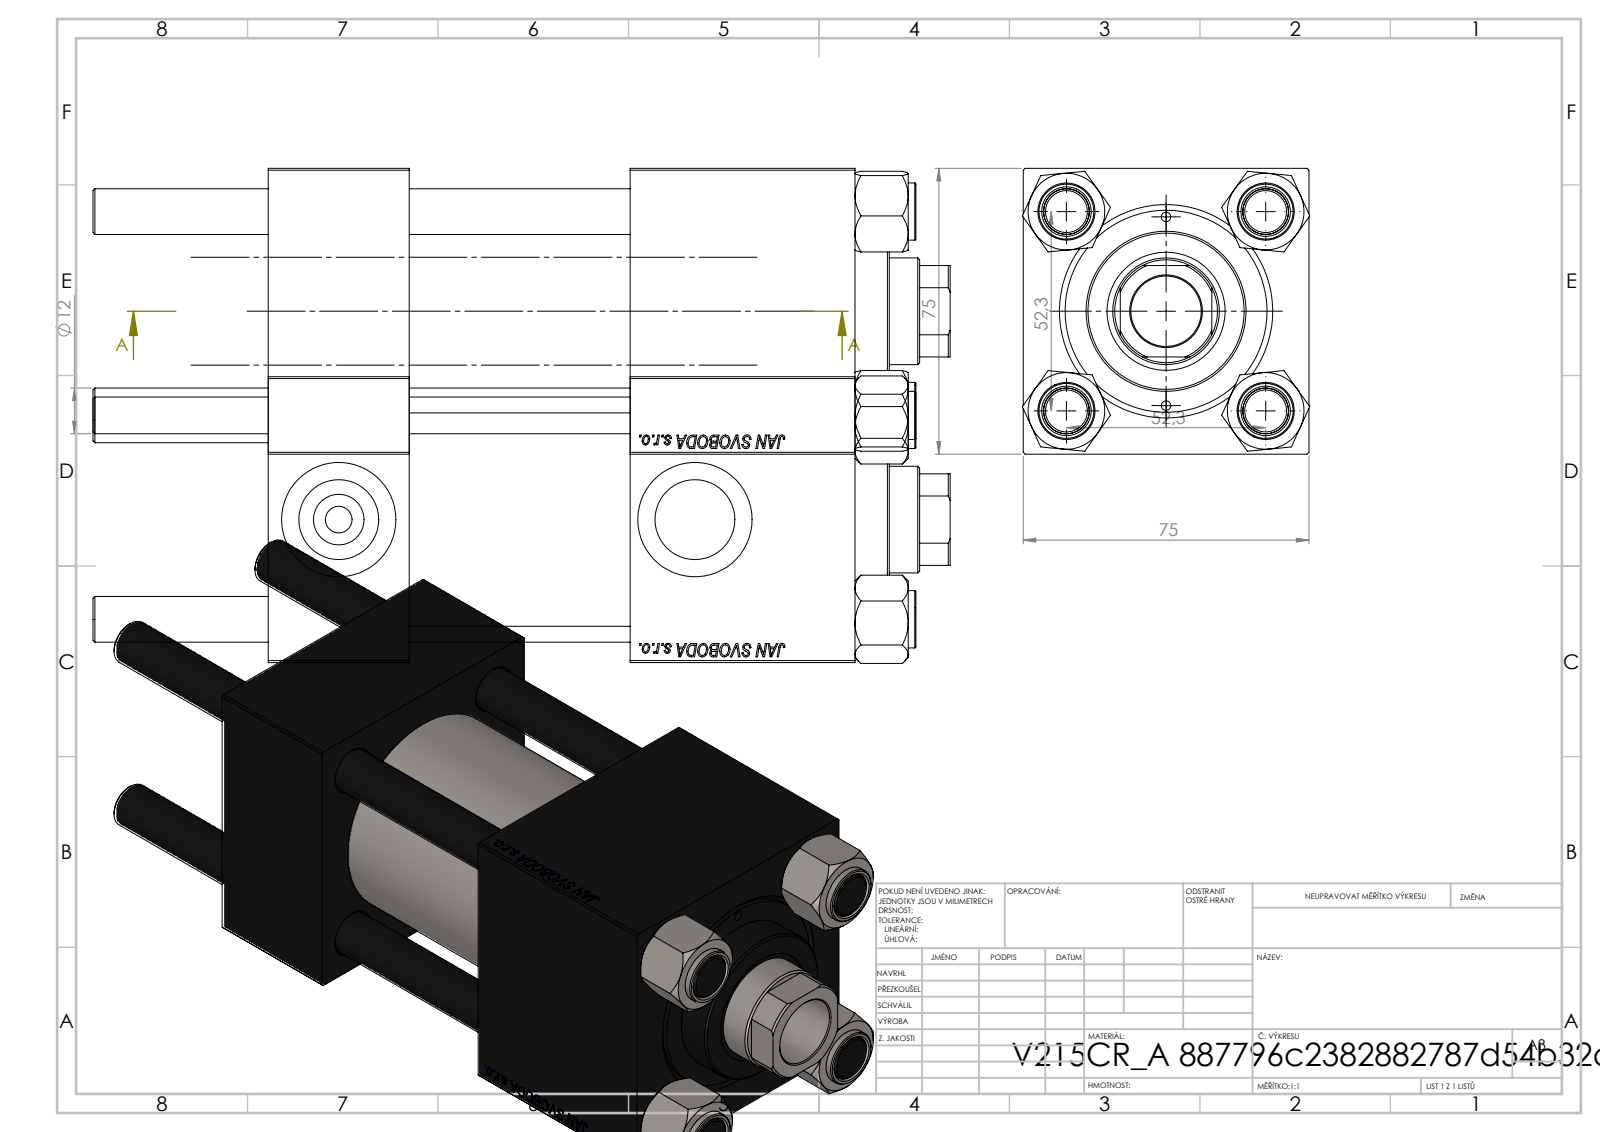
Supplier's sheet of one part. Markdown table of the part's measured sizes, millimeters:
| quantity | value |
| --- | --- |
| part name | V215_VC_A; V215CR_VCP; V215CR_BODY_A; NUT_M5 (+1 more) |
| STEP written by | SolidWorks 2019 (CONFIG_CONTROL_DESIGN) |
| units | millimeters |
| bodies | 11 solids, 1140 faces (522 planar, 82 cylindrical, 536 other) |
| overall size | 225 × 75.43 × 75 |
| volume | 702 162 mm³ |
| surface area | 167 467 mm² |
| round holes (diameter × count) | 12 × 4, 2.5 × 2, 7 × 2, 20.96 × 2, 30 × 2, 18.5 × 1, 28 × 1, 31 × 1, 41 × 1, 50 × 1, 53 × 1 |
| round bosses / shafts (diameter × count) | 15 × 4, 56 × 1, 42 × 1 |
| partial cylindrical surfaces (radius × count) | 13.5 × 1 |
| main face-to-face distances | 75, 37, 154, 117, 95, 58, 59, 125.3, 88.3, 30.3 |
| hole center spacings | 26.19, 36.98, 52.3, 57.22, 24.75, 73.96, 49.5, 93.5 |
